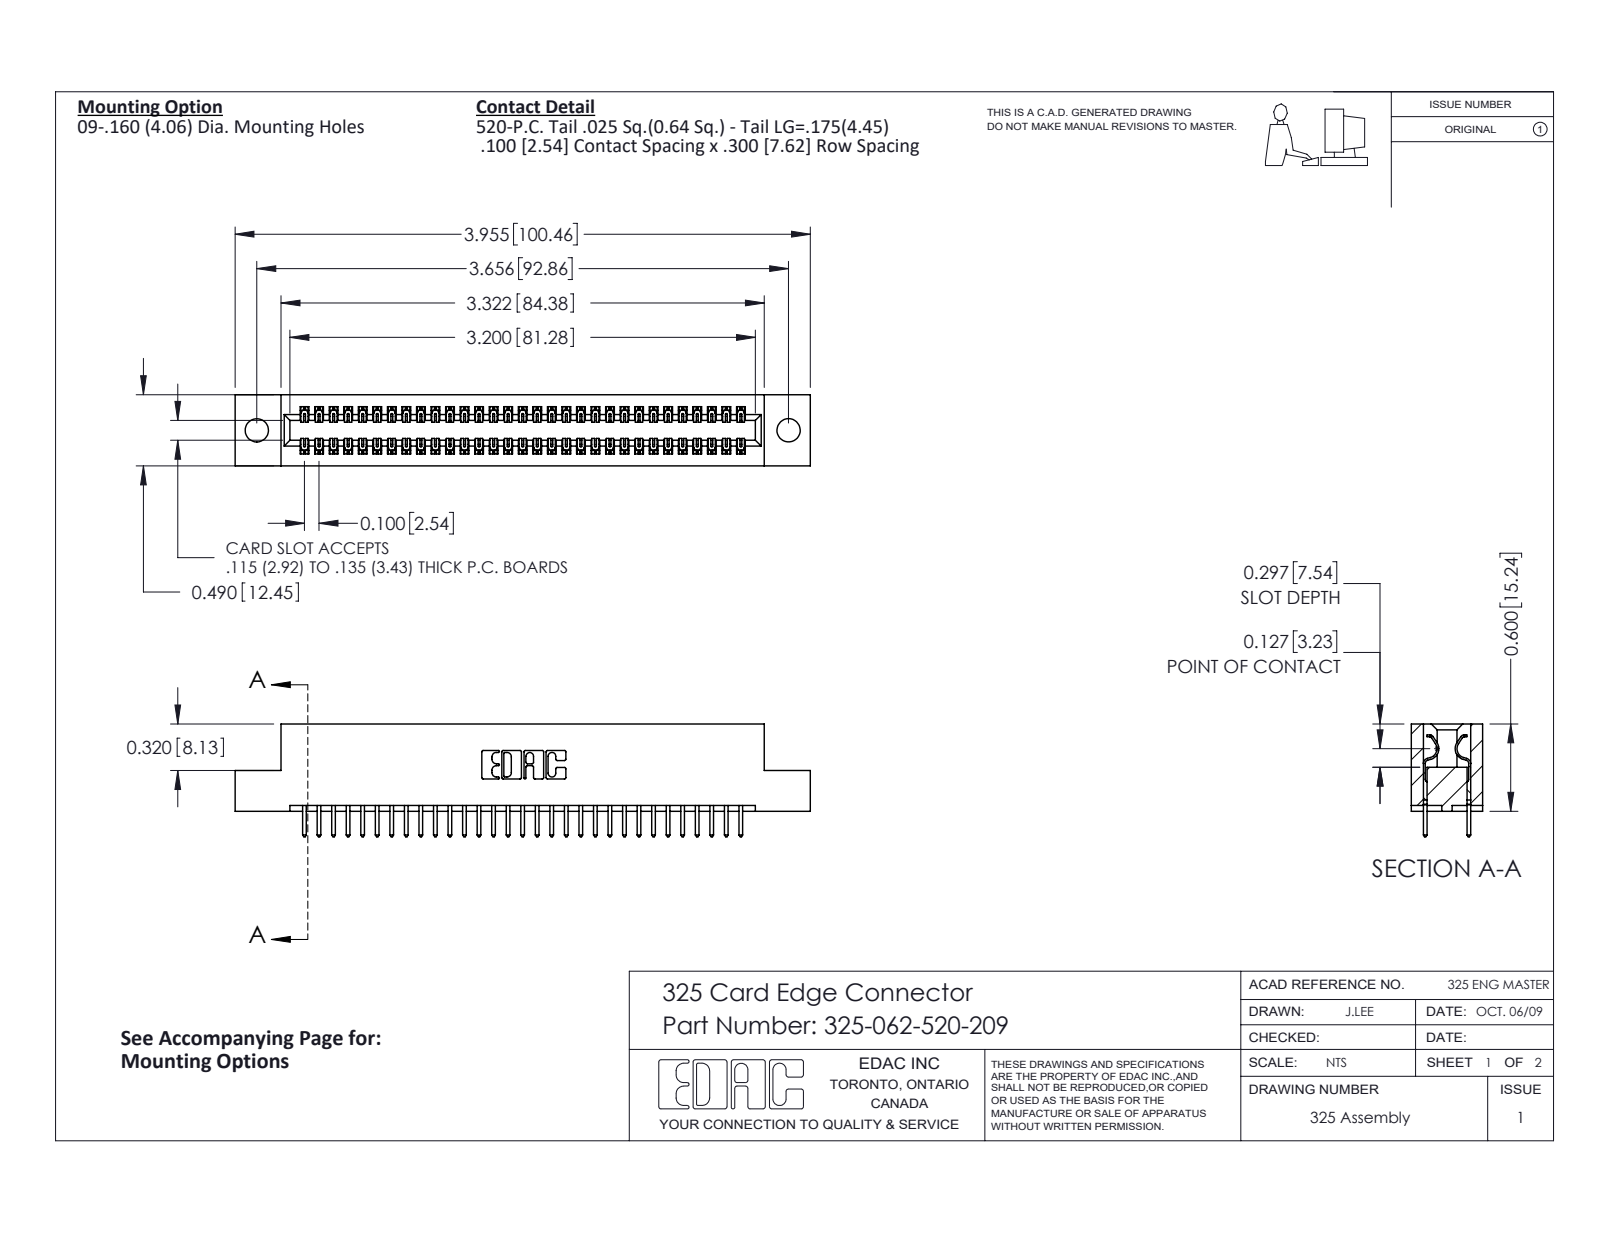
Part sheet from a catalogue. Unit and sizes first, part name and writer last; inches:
Units: inches
Overall size (bounding box): 3.955 × 0.775 × 0.49
Round holes (diameter × count): ⌀0.16 ×2
Partial cylindrical surfaces — rounded edges, fillets, slot ends (radius × count): R0.006 ×93, R0.01 ×62, R0.01 ×22, R0.007 ×6, R0.031 ×6, R0.026 ×3, R0.014 ×2, R0.022 ×2
Main face-to-face distances: 0.083, 0.407, 0.3, 0.49, 0.107, 0.383, 0.025, 0.325, 0.04, 0.275
Hole centre spacings: 3.656
Volume: 0.771 in³ · Surface area: 22.97 in²
Bodies: 63 solids, 3338 faces (2302 planar, 1036 cylindrical, 0 other)
Part name (STEP PRODUCT): 325-292-001_325-293-120; 325 Part_.160 TH; 325-062-520-209
STEP written by: SolidWorks 2016 (CONFIG_CONTROL_DESIGN)
